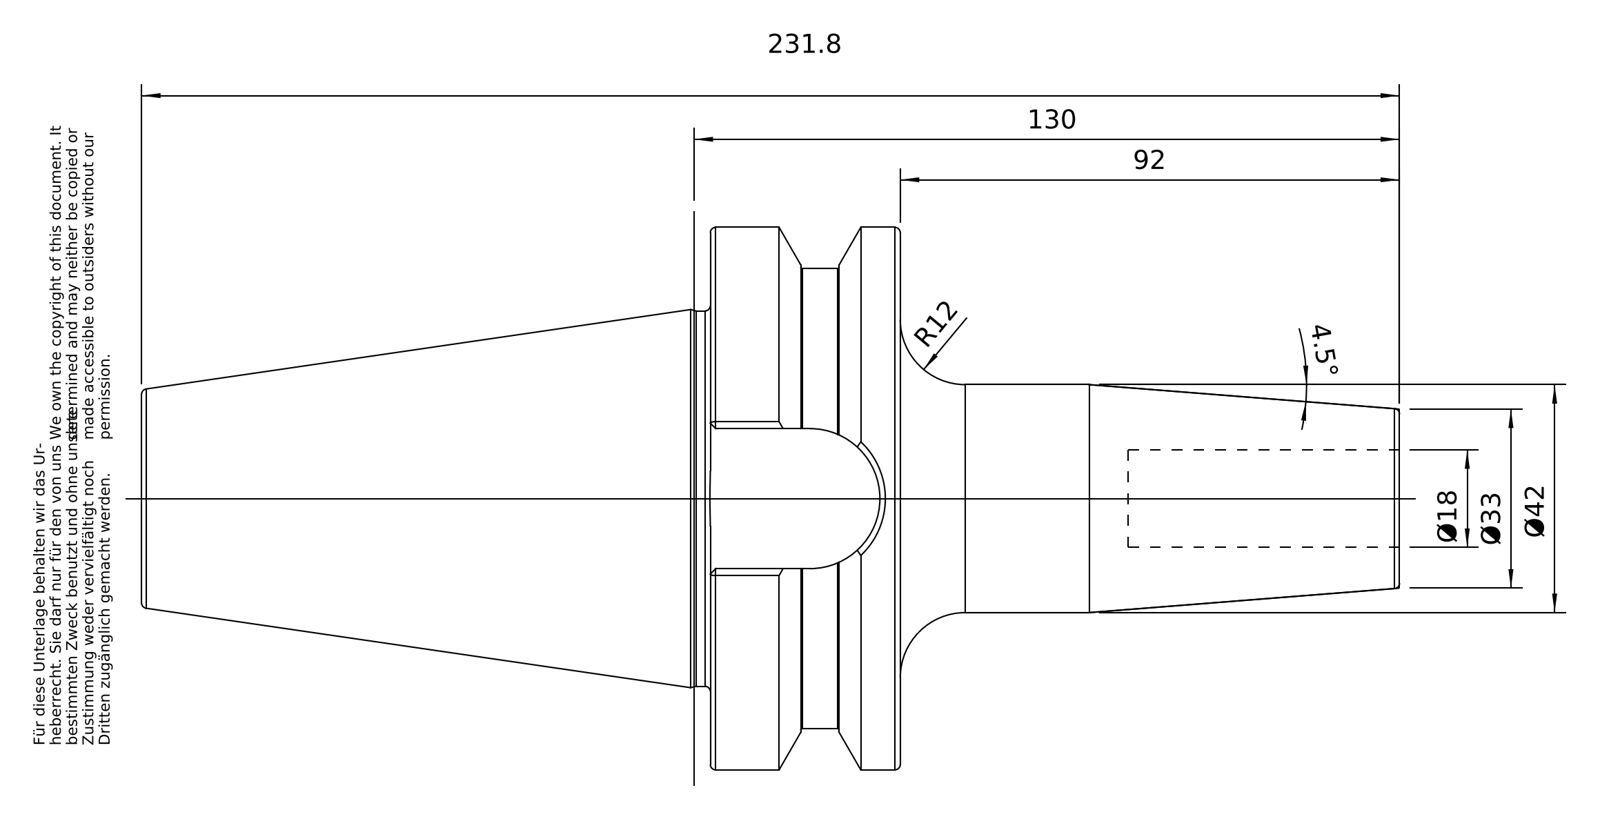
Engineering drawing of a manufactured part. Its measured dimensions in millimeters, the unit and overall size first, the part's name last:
Units: millimetres
Overall size (bounding box): 231.8 × 99.97 × 99.97
Round holes (diameter × count): ⌀18 ×1, ⌀20.75 ×1, ⌀25.02 ×1, ⌀25.7 ×1
Round bosses / shafts (diameter × count): ⌀99.97 ×1, ⌀84.75 ×1, ⌀69.15 ×1, ⌀42 ×1, ⌀24.01 ×1
Partial cylindrical surfaces — rounded edges, fillets, slot ends (radius × count): R12.9 ×1
Main face-to-face distances: 35, 70.4, 127, 92, 104.8, 139.8, 231.8, 25.8, 181.8, 77
Volume: 571 601 mm³ · Surface area: 64 844 mm²
Bodies: 1 solid, 96 faces (26 planar, 22 cylindrical, 48 other)
Part name (STEP PRODUCT): 50-644-18
STEP written by: PRO/ENGINEER BY PARAMETRIC TECHNOLOGY CORPORATION, 2010430 (CONFIG_CONTROL_DESIGN)
